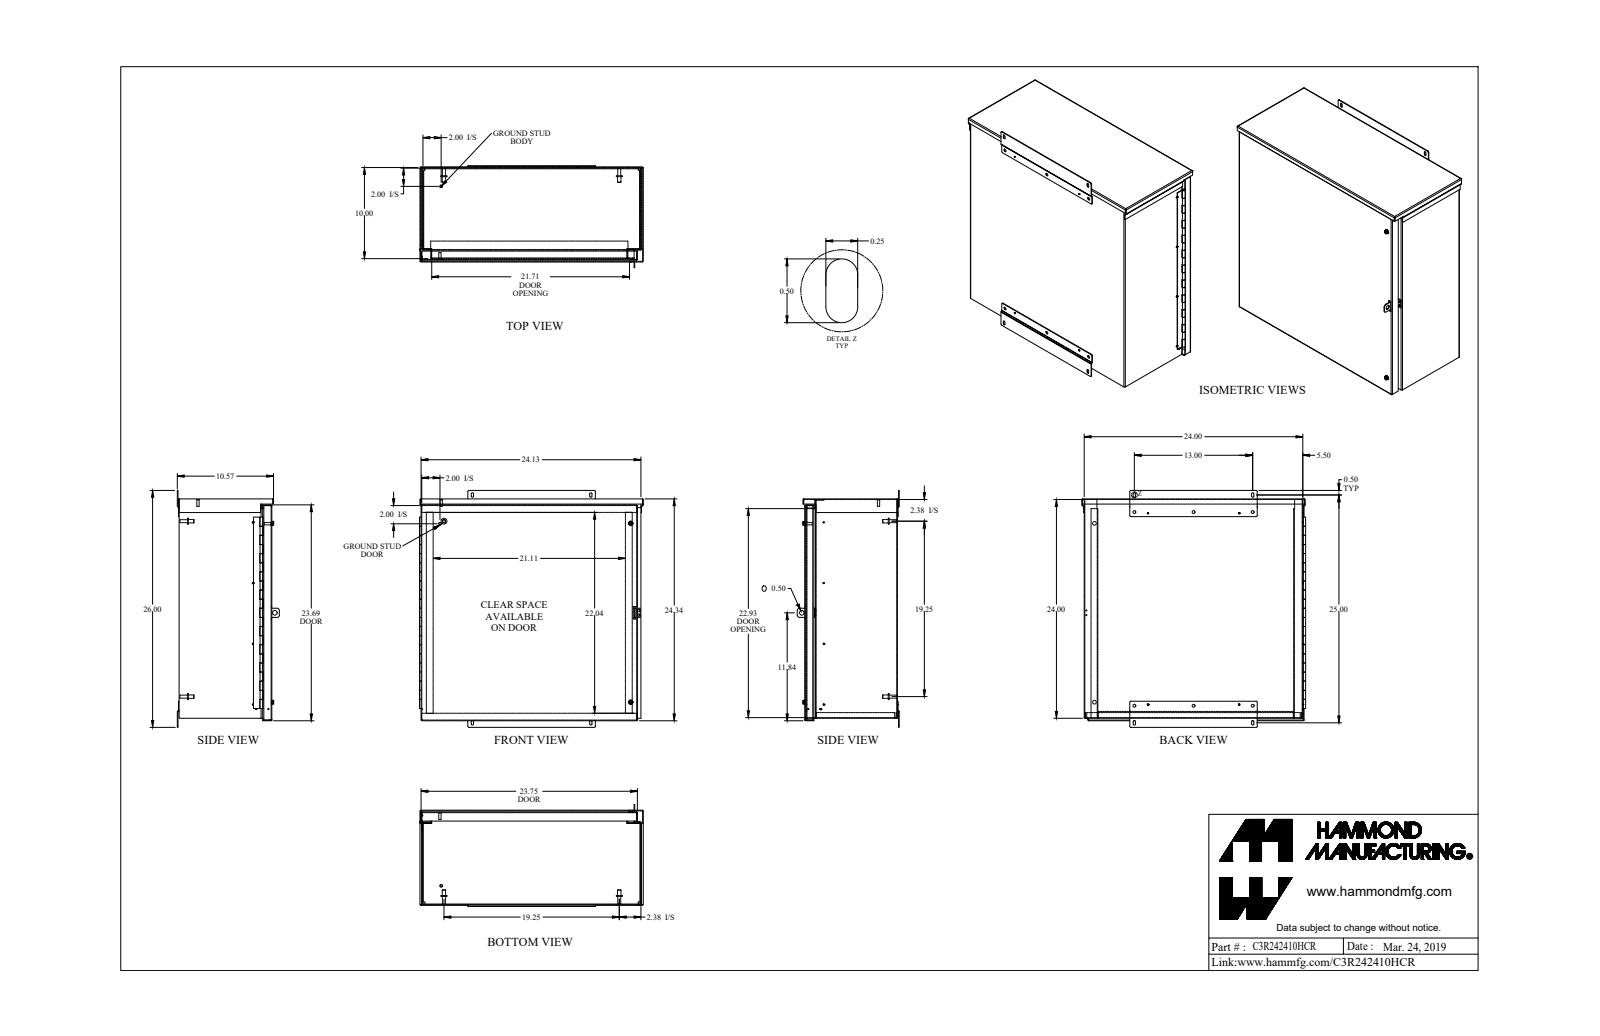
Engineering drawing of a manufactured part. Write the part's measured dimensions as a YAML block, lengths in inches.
part_name: "C3R242410HCR_Default"
step_written_by: "SolidWorks 2019 (CONFIG_CONTROL_DESIGN)"
units: inches
bodies: {solids: 33, faces: 888, planar: 499, cylindrical: 335, other: 54}
overall_size: [26, 24.571, 11.197]
volume: 196
surface_area: 5308
round_holes:
  - {diameter: 0.313, count: 9}
  - {diameter: 0.137, count: 4}
  - {diameter: 0.14, count: 4}
  - {diameter: 0.26, count: 3}
  - {diameter: 0.266, count: 2}
  - {diameter: 0.28, count: 2}
  - {diameter: 0.29, count: 2}
  - {diameter: 0.397, count: 2}
  - {diameter: 0.188, count: 1}
  - {diameter: 0.5, count: 1}
round_bosses_or_shafts:
  - {diameter: 0.131, count: 10}
  - {diameter: 0.65, count: 4}
  - {diameter: 0.375, count: 4}
  - {diameter: 0.33, count: 4}
  - {diameter: 0.51, count: 3}
  - {diameter: 0.244, count: 3}
  - {diameter: 0.187, count: 3}
  - {diameter: 0.5, count: 2}
partial_cylinders:
  - {radius: 0.036, count: 31}
  - {radius: 0.108, count: 31}
  - {radius: 0.125, count: 19}
  - {radius: 0.171, count: 3}
  - {radius: 0.25, count: 2}
face_to_face_distances: [0.072, 10.1, 24, 23.928, 10.028, 10.172, 24.072, 23.856, 0.928, 1]
hole_center_spacings: [1.505, 5.002, 6.5, 11.501, 21.178, 21.709, 22.222, 24.052]
